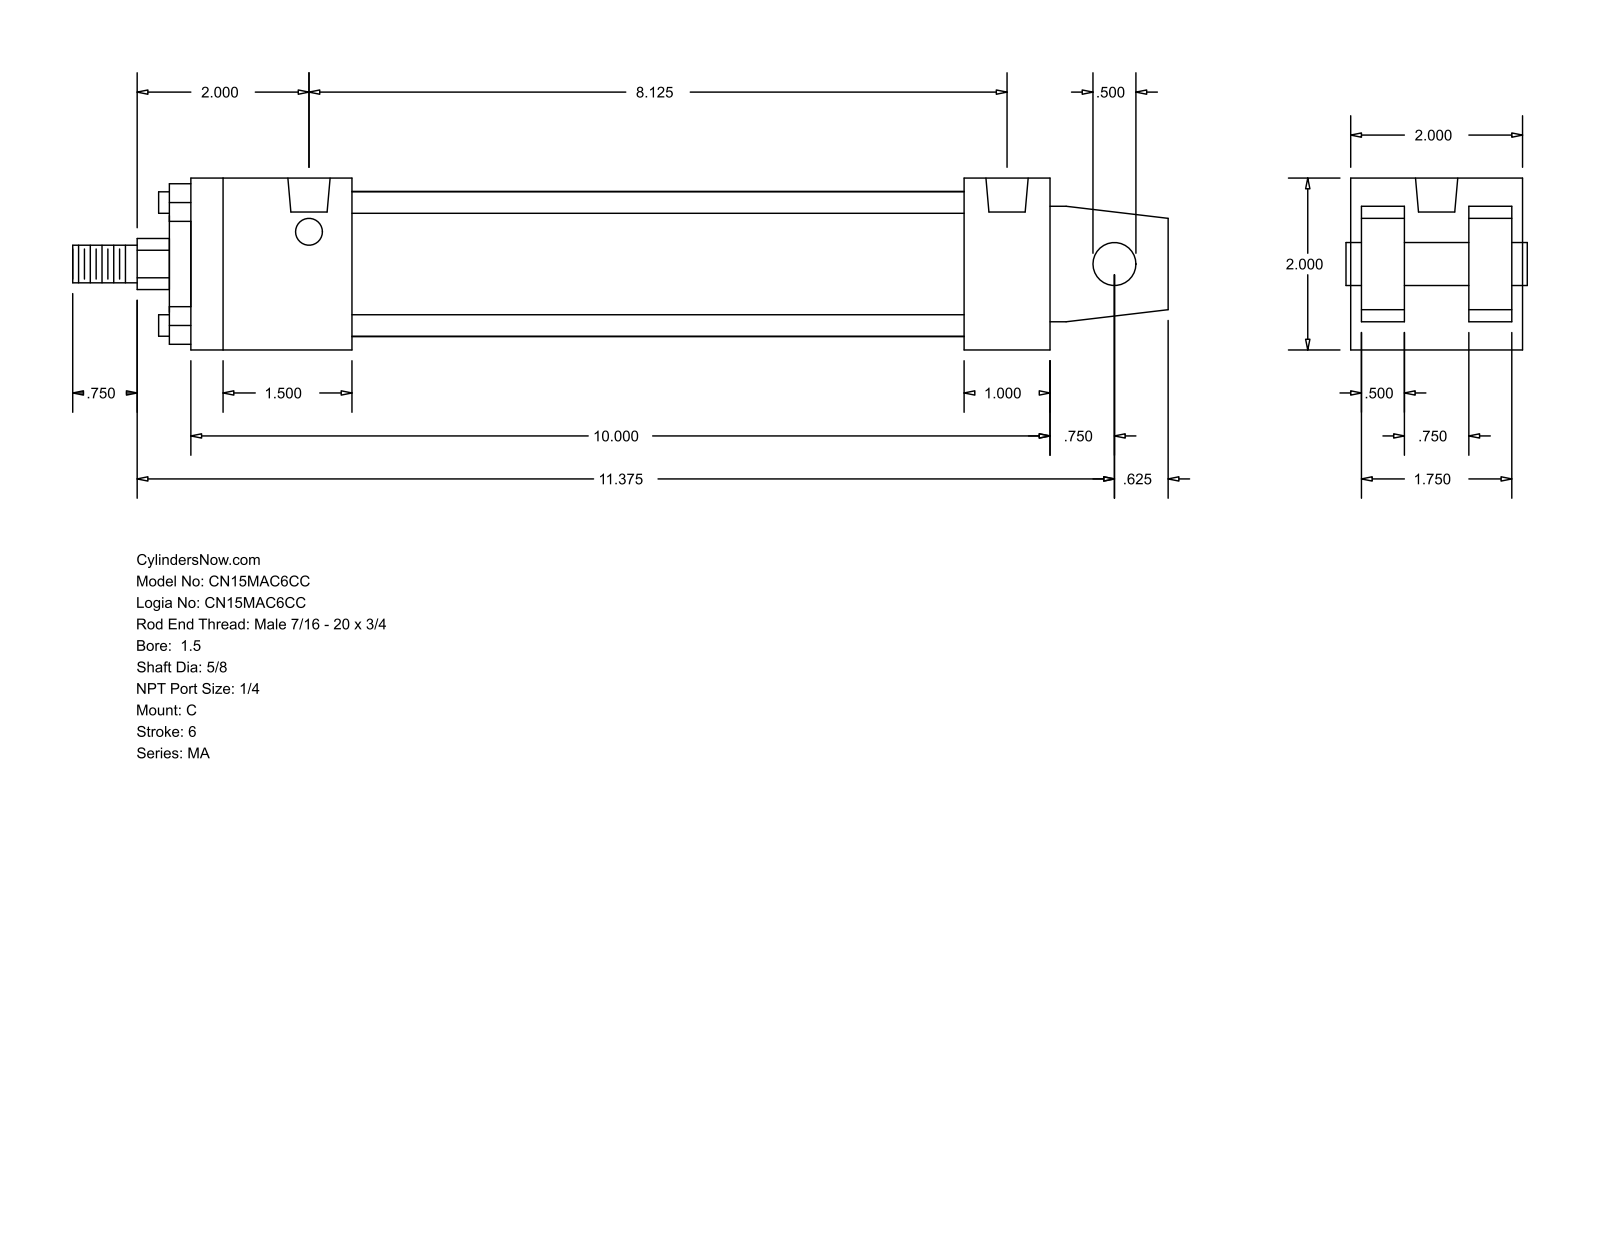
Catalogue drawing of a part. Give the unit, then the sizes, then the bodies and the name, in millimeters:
Units: millimetres
Overall size (bounding box): 323.85 × 50.8 × 50.8
Round holes (diameter × count): ⌀7.94 ×4, ⌀12.49 ×2
Round bosses / shafts (diameter × count): ⌀6.35 ×4, ⌀42.93 ×1, ⌀28.57 ×1, ⌀15.88 ×1, ⌀12.7 ×1, ⌀11.11 ×1
Partial cylindrical surfaces — rounded edges, fillets, slot ends (radius × count): R7.54 ×1
Main face-to-face distances: 50.8, 12.7, 34.93, 15.87, 3.17, 47.63, 31.76, 254, 228.59, 25.41
Hole centre spacings: 206.38
Bodies: 0 solids, 103 faces (76 planar, 27 cylindrical, 0 other)
Part name (STEP PRODUCT): MA_C__0150_0.625
STEP written by: GSSL Pune (CONFIG_CONTROL_DESIGN)
